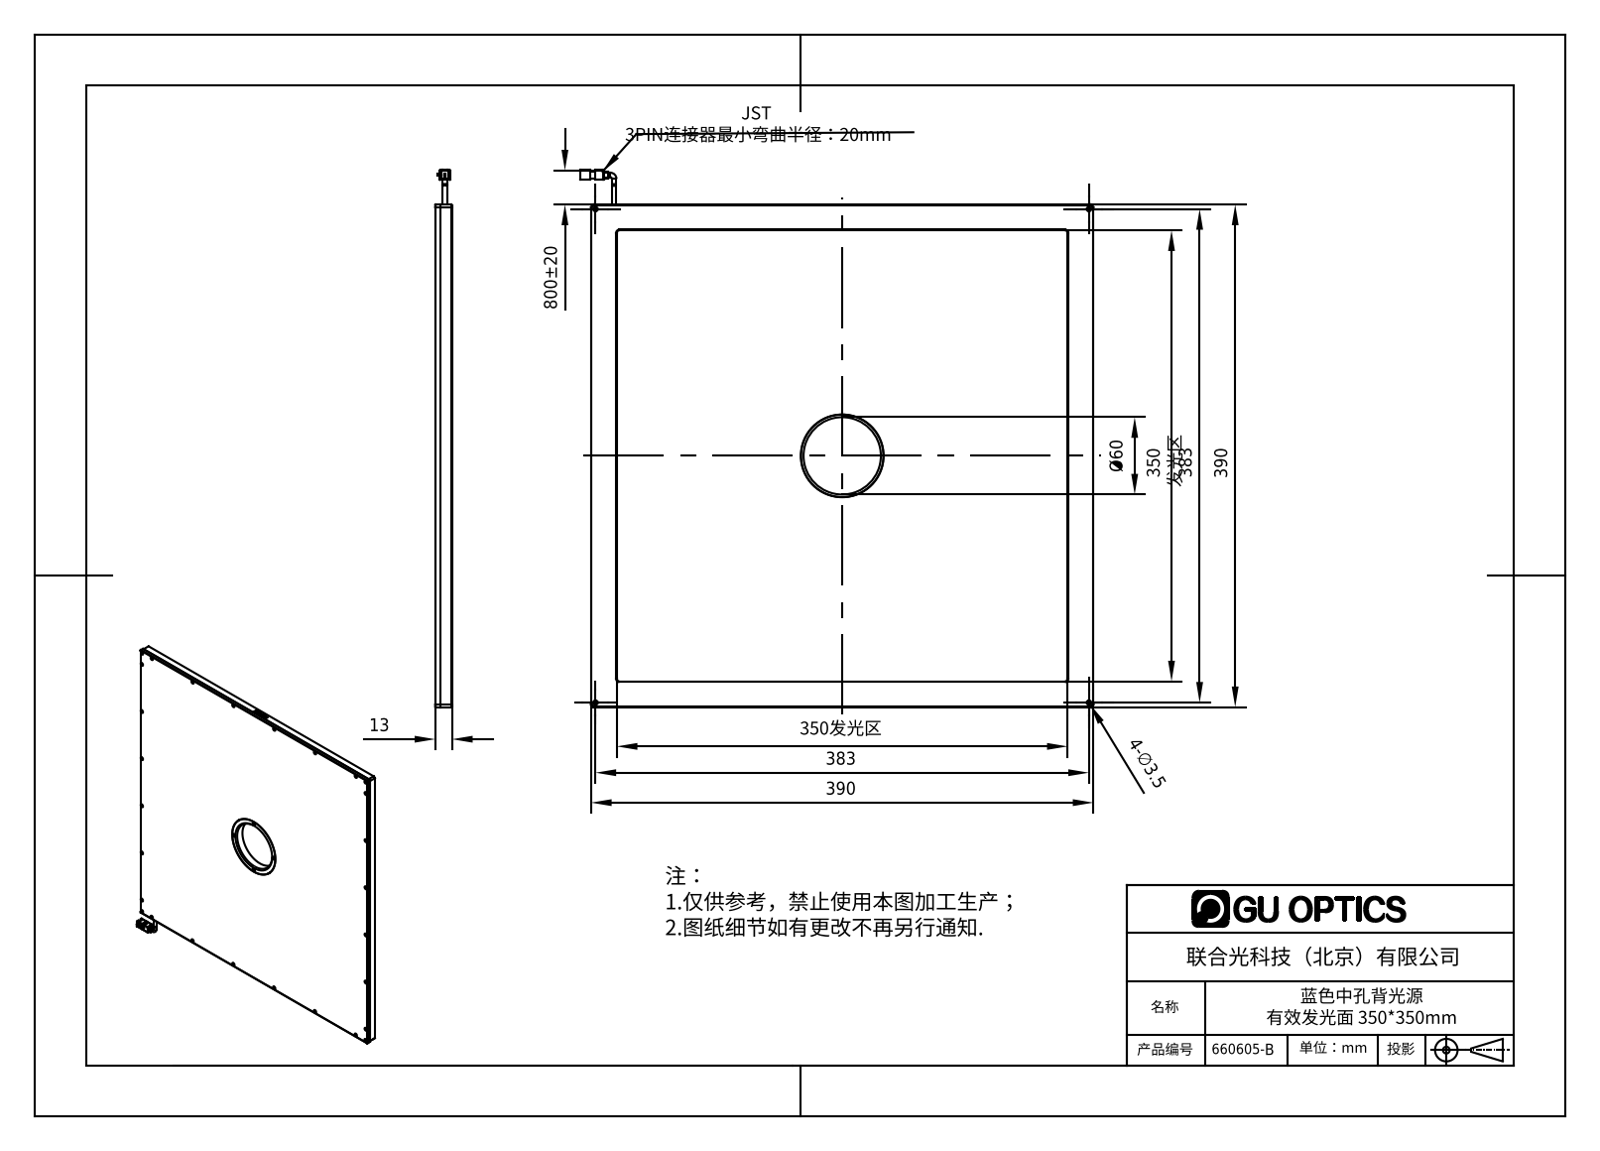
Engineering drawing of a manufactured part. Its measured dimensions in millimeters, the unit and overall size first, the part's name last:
Units: millimetres
Overall size (bounding box): 417 × 398.5 × 13
Round holes (diameter × count): ⌀2.4 ×28, ⌀1.6 ×24, ⌀3.5 ×4, ⌀60 ×1, ⌀64.2 ×1, ⌀74 ×1
Round bosses / shafts (diameter × count): ⌀3.5 ×2, ⌀73.8 ×1, ⌀64 ×1
Partial cylindrical surfaces — rounded edges, fillets, slot ends (radius × count): R0.5 ×8, R2 ×8, R1 ×4, R3 ×4, R1.5 ×2
Main face-to-face distances: 4, 6, 10, 9, 3, 13, 0.5, 6.5, 2.5, 10.5
Hole centre spacings: 70, 390.33, 140, 408.72, 210, 384, 437.67, 16.51
Volume: 1 515 000 mm³ · Surface area: 673 989 mm²
Bodies: 6 solids, 510 faces (177 planar, 170 cylindrical, 163 other)
Part name (STEP PRODUCT): 660605-B
STEP written by: SolidWorks 2016 (AUTOMOTIVE_DESIGN)
